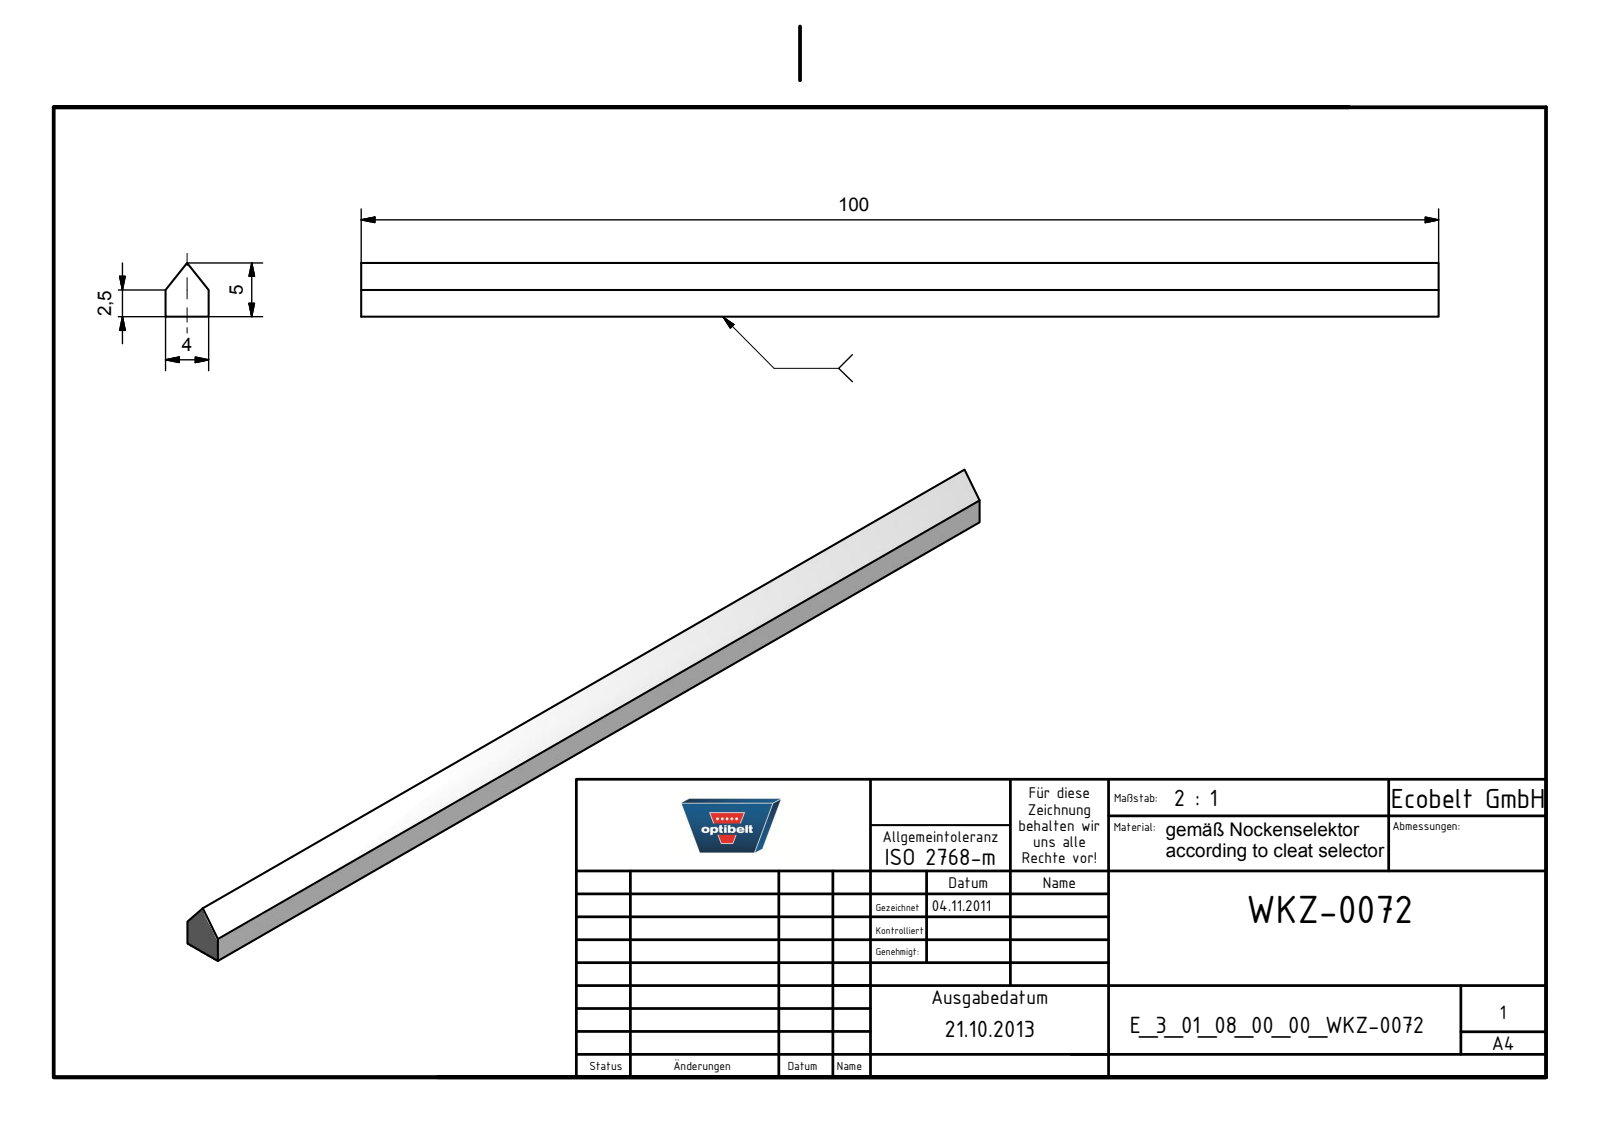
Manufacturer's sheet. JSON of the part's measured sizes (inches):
{"part_name": "E_3_01_08_00_00_WKZ-0072", "step_written_by": "Autodesk Inventor 2025 (AUTOMOTIVE_DESIGN)", "units": "inches", "bodies": {"solids": 1, "faces": 7, "planar": 7, "cylindrical": 0, "other": 0}, "overall_size": [3.937, 0.197, 0.157], "volume_in3": 0.092, "surface_area_in2": 2.434, "face_to_face_distances": [0.157, 3.937]}
